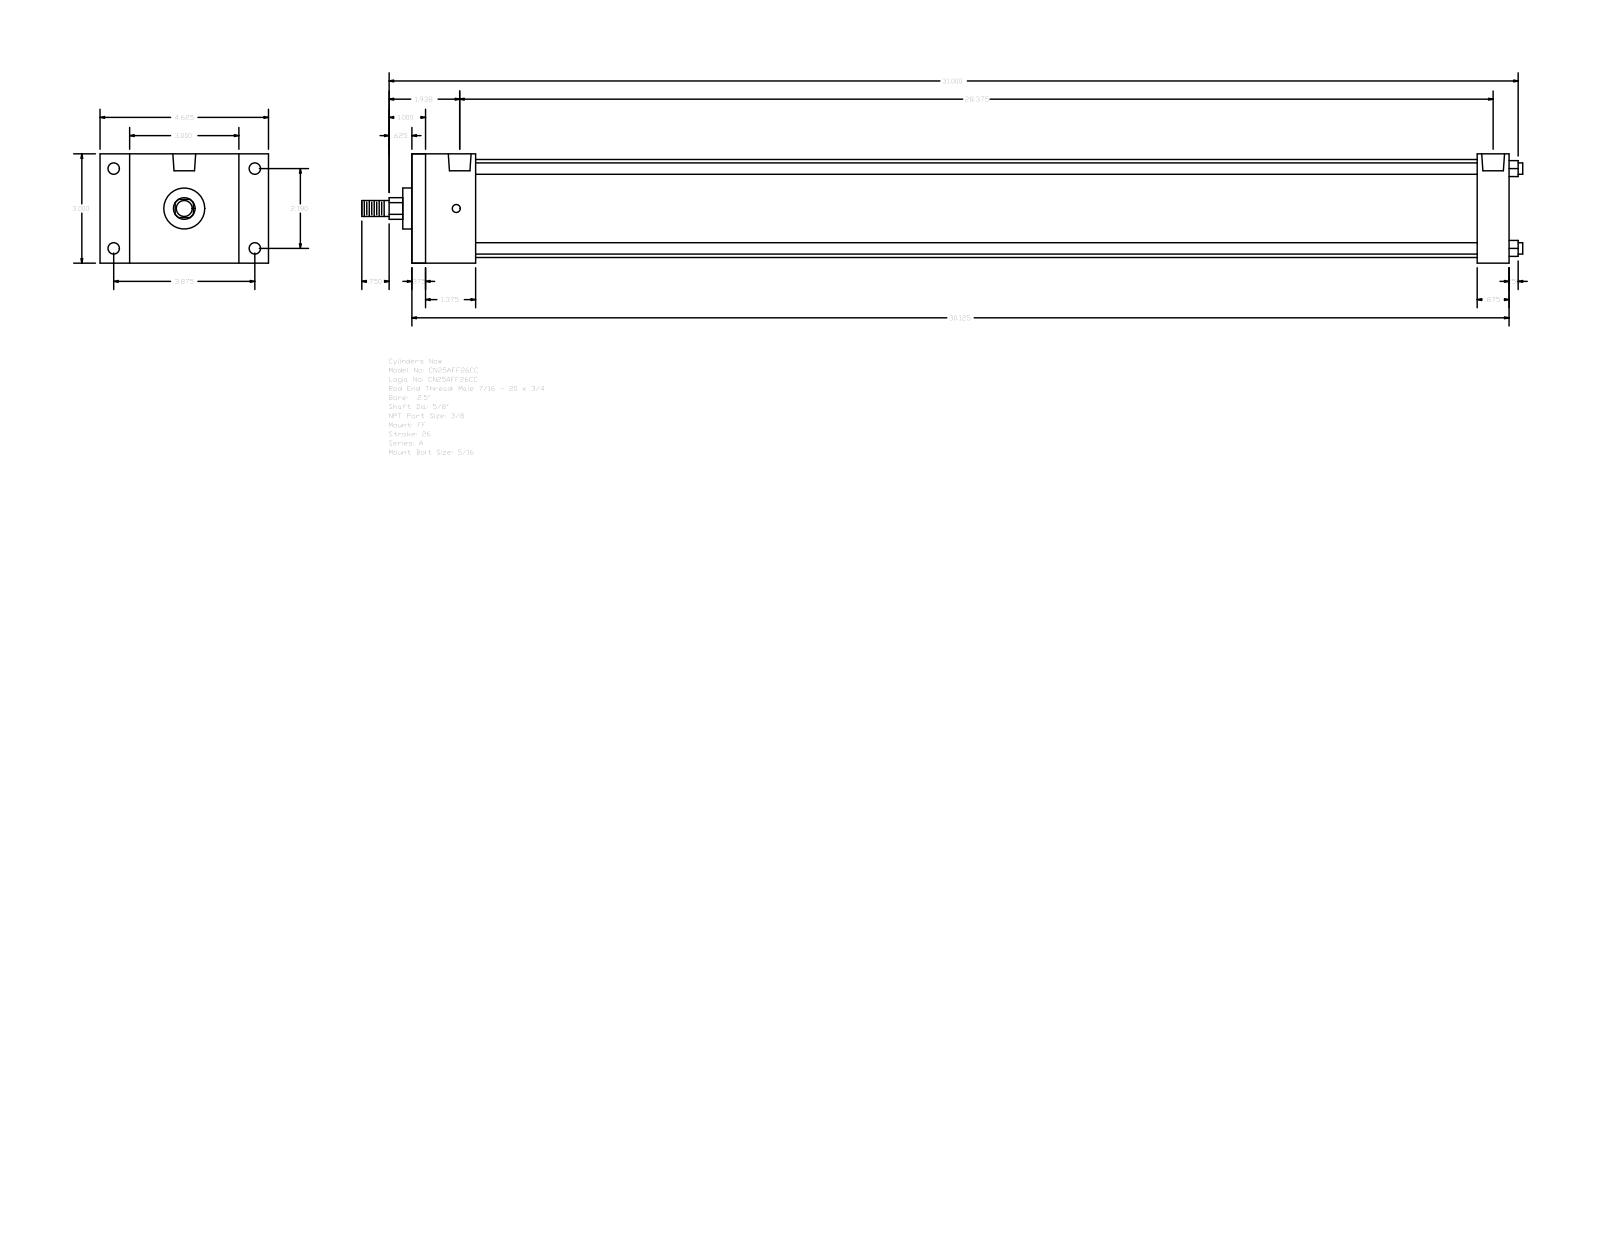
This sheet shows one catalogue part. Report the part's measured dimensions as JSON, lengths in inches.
{"part_name": "A_FF__0250_0.625", "step_written_by": "GSSL Pune (CONFIG_CONTROL_DESIGN)", "units": "inches", "bodies": {"solids": 0, "faces": 92, "planar": 64, "cylindrical": 28, "other": 0}, "overall_size": [31.875, 4.625, 3], "round_holes": [[0.219, 4], [0.313, 4], [0.627, 2]], "round_bosses_or_shafts": [[0.313, 4], [2.69, 1], [1.125, 1], [0.625, 1], [0.437, 1]], "partial_cylinders_radius": [[0.297, 1]], "face_to_face_distances": [3, 30.125, 0.375, 29.75, 1.75, 1.375, 29.25, 28.875, 27.5, 28.375], "hole_center_spacings": [0.094, 2.19, 3.875, 4.451, 28.469, 28.563, 28.375]}
